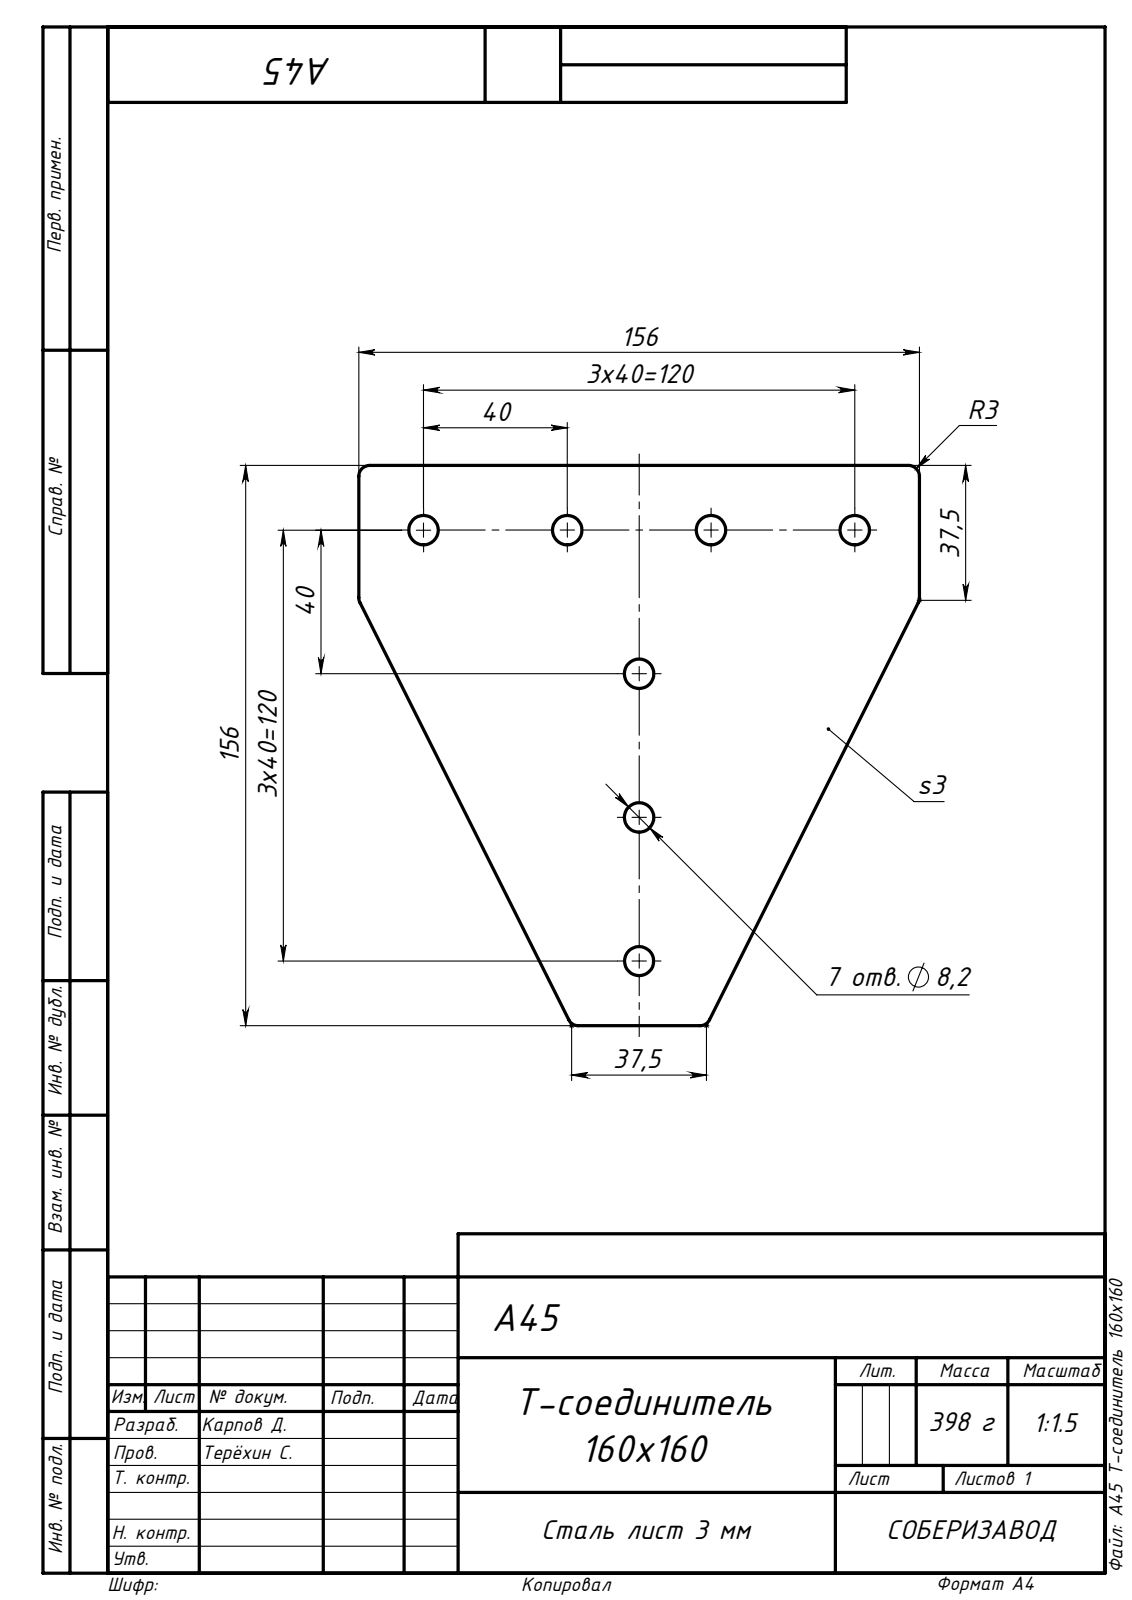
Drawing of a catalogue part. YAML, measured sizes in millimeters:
part_name: "A45 Т-соединитель 160х160"
step_written_by: "SolidWorks 2019 (AUTOMOTIVE_DESIGN)"
units: millimeters
bodies: {solids: 1, faces: 28, planar: 8, cylindrical: 20, other: 0}
overall_size: [156, 156, 3]
volume: 50834
surface_area: 36020
round_holes:
  - {diameter: 8.2, count: 6}
  - {diameter: 8.1, count: 1}
partial_cylinders:
  - {radius: 3, count: 6}
face_to_face_distances: [3, 156]
hole_center_spacings: [40, 80, 44.72, 72.11, 82.46, 100, 121.66, 134.16]
